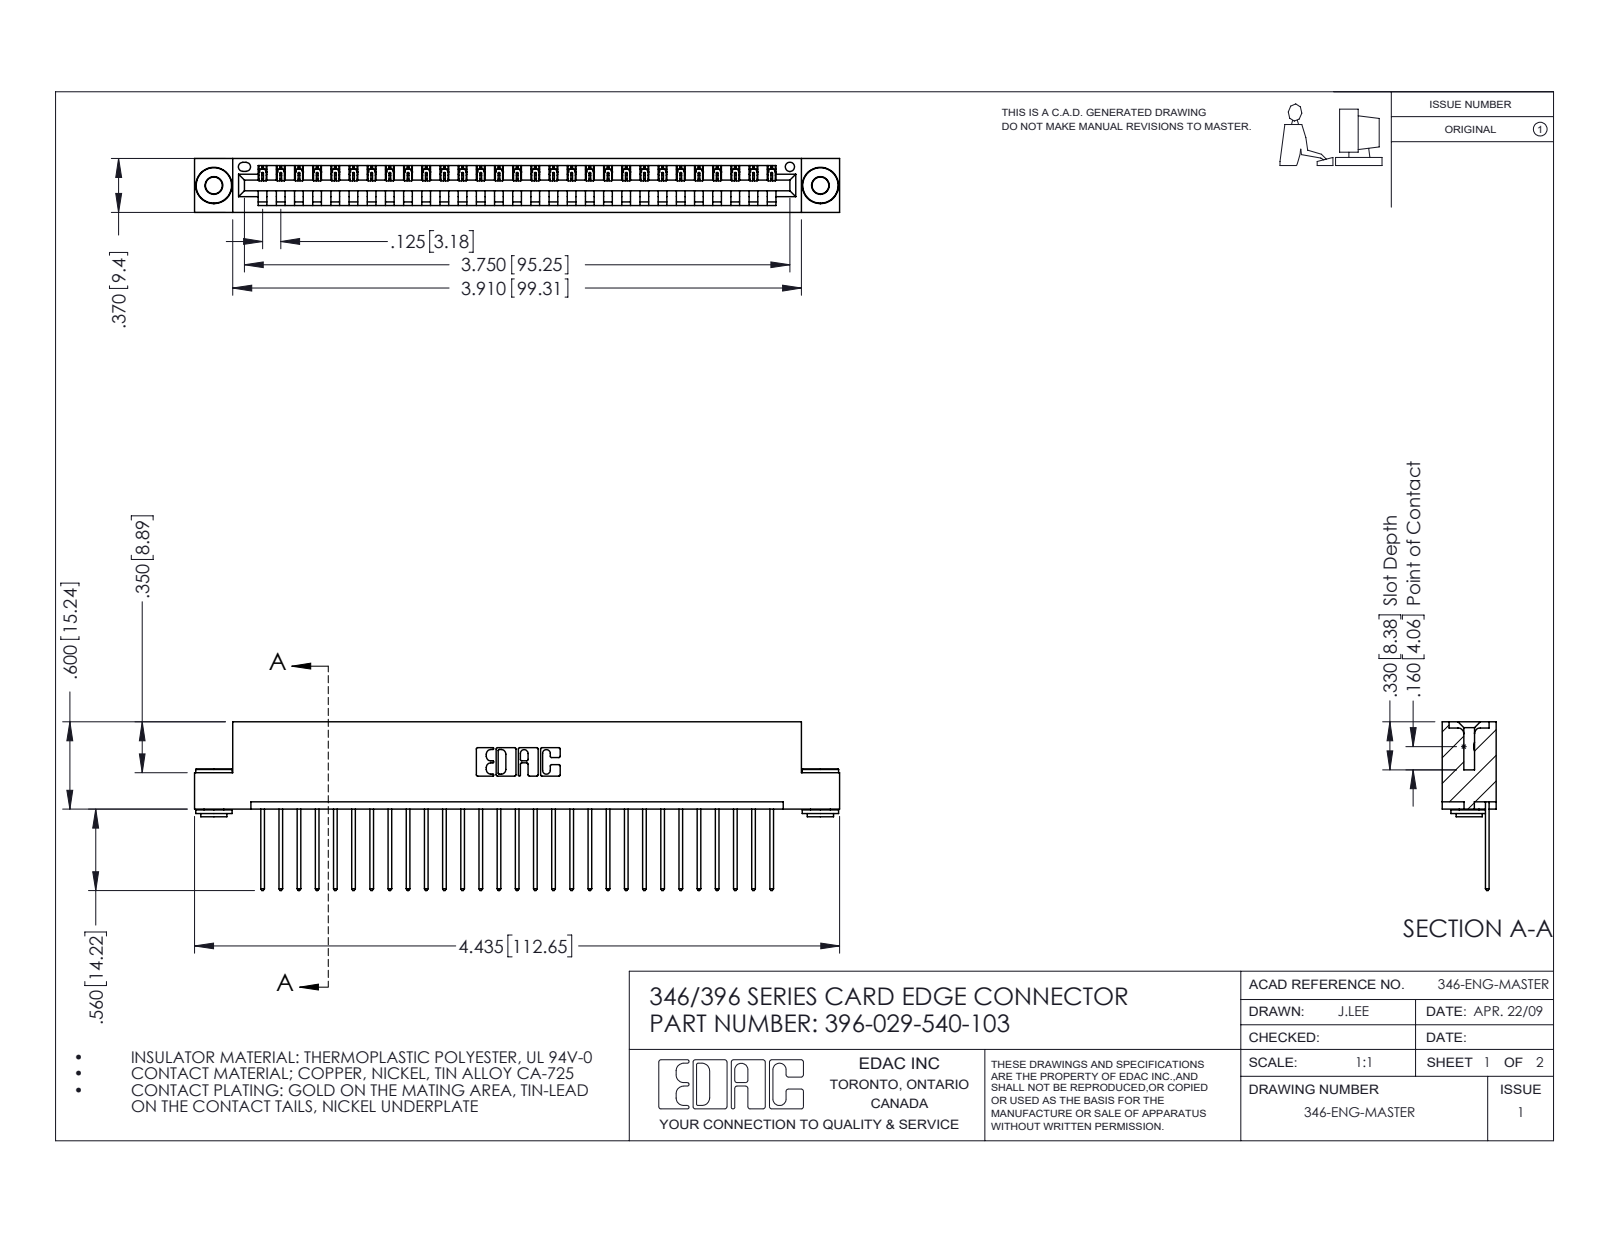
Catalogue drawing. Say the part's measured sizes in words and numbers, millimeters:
The part is named "396-029-540-103; 345-292-001_345-293-140; 346 Part_Flush Mounting Lugs - 0.156 Dia-TH; 345-250-002_345-250-002-102". Its 3-D file was written by "SolidWorks 2016 (CONFIG_CONTROL_DESIGN)". It is 32 solids with 1842 faces: 1246 planar, 588 cylindrical and 8 other. Overall it measures 112.6 by 29.5 by 9.4 millimeters. Its volume is 10 700 cubic millimeters and its surface area 13 810 square millimeters. Round holes: 2 of diameter 2.9, 2 of diameter 4, 1 of diameter 1.6. Round bosses or shafts: 2 of diameter 6.4, 2 of diameter 4.6, 2 of diameter 3.5. Partial cylindrical surfaces (rounded edges, fillets, slot ends): 58 of radius 0.2, 58 of radius 0.3, 22 of radius 0.3, 6 of radius 0.2, 6 of radius 0.8, 3 of radius 0.7, 2 of radius 0.8, 2 of radius 1. The main face-to-face distances are 1.2, 8.2, 6.4, 9.4, 0.6, 1.8, 7.6, 3.8, 5.6, 2.5. The hole center spacings are 6.2, 100.6, 105.9.
